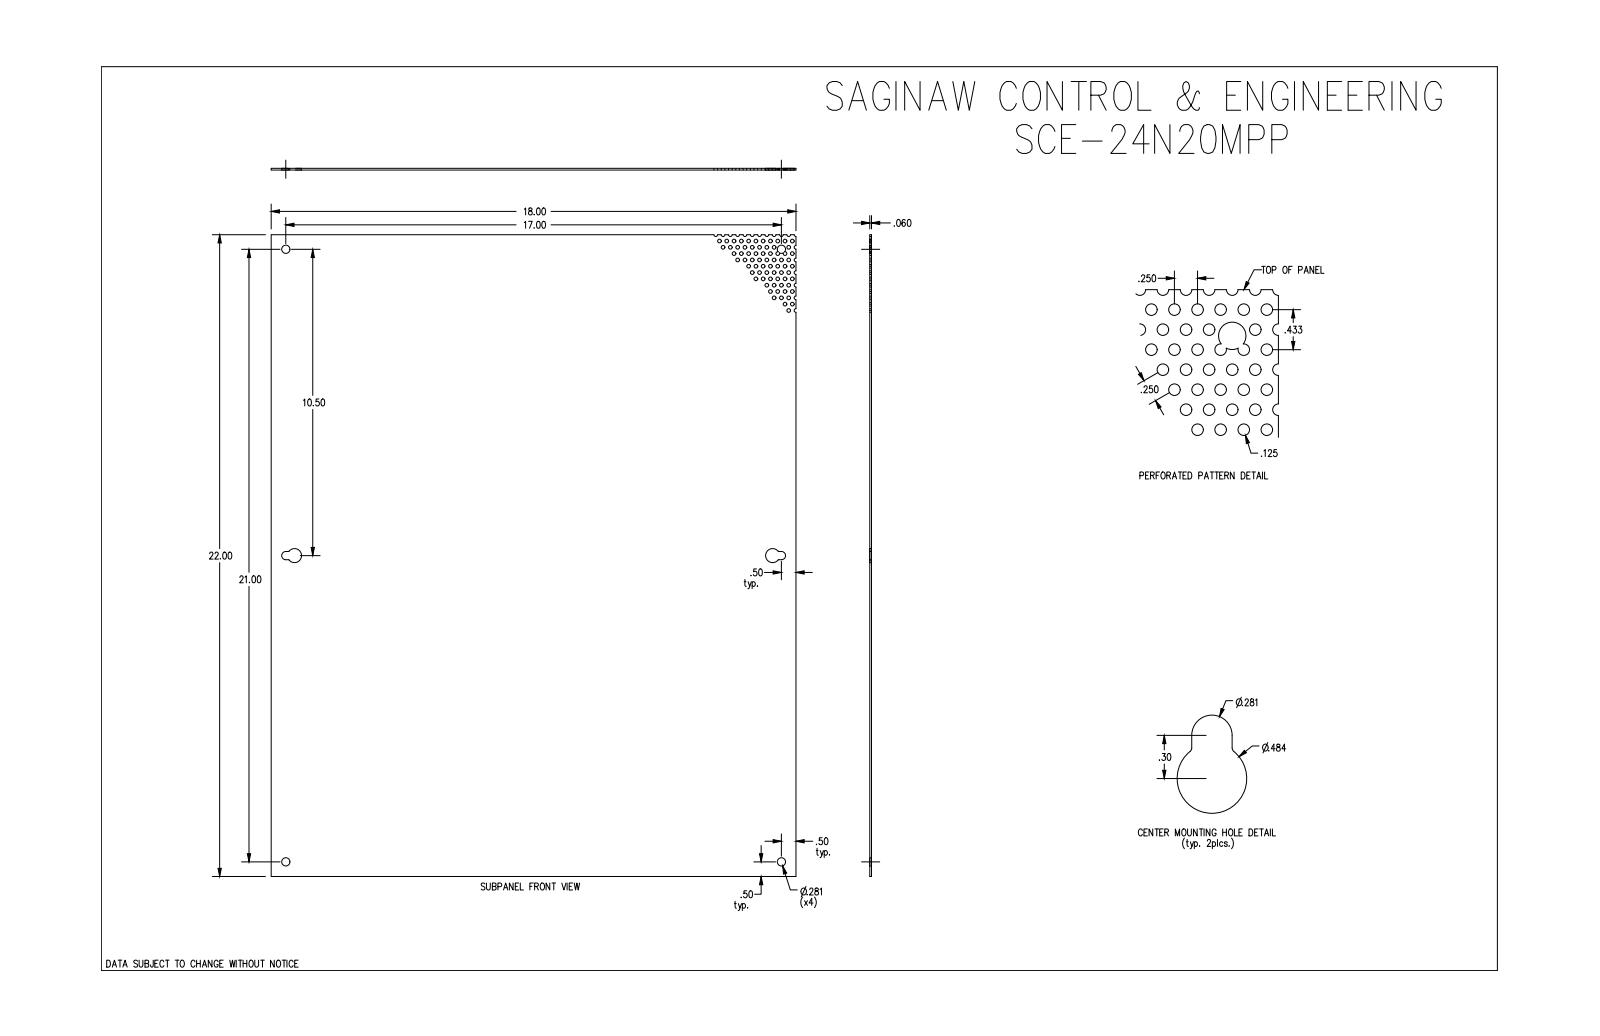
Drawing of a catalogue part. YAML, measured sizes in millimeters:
part_name: "SCE-24N20MPP"
step_written_by: "SolidWorks 2019 (CONFIG_CONTROL_DESIGN)"
units: millimeters
bodies: {solids: 1, faces: 128, planar: 27, cylindrical: 101, other: 0}
overall_size: [558.8, 457.2, 1.5]
volume: 387700
surface_area: 513300
round_holes:
  - {diameter: 3.2, count: 70}
  - {diameter: 7.1, count: 4}
partial_cylinders:
  - {radius: 1.6, count: 18}
  - {radius: 0.8, count: 4}
  - {radius: 3.6, count: 2}
  - {radius: 6.1, count: 2}
face_to_face_distances: [1.5, 457.2, 558.8, 275.8, 283, 7.1]
hole_center_spacings: [6.4, 16.8, 12.7, 11, 11, 33.6, 27.7, 19.1]
